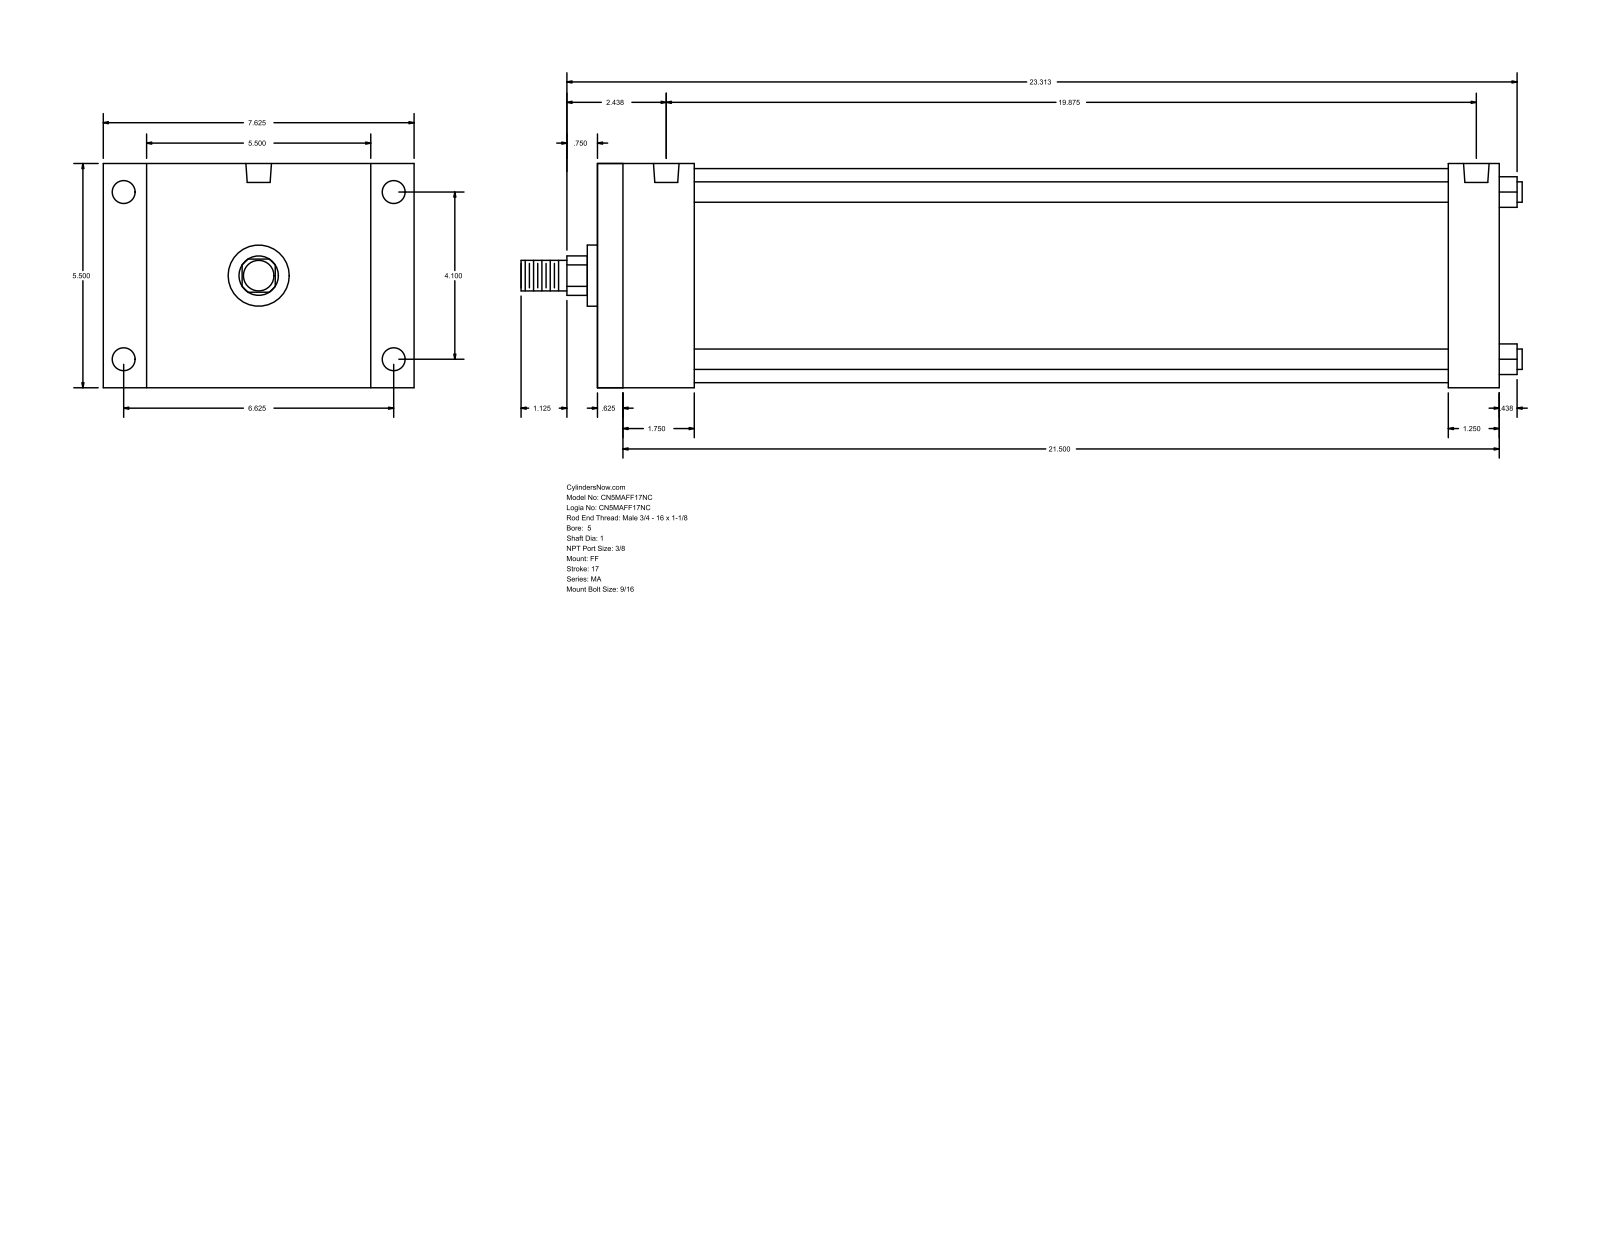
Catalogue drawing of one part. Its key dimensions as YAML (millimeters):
part_name: "MA_FF__0500_1"
step_written_by: "GSSL Pune (CONFIG_CONTROL_DESIGN)"
units: millimeters
bodies: {solids: 0, faces: 92, planar: 64, cylindrical: 28, other: 0}
overall_size: [623.89, 193.68, 139.7]
round_holes:
  - {diameter: 11.11, count: 4}
  - {diameter: 14.29, count: 4}
  - {diameter: 15.93, count: 2}
round_bosses_or_shafts:
  - {diameter: 12.7, count: 4}
  - {diameter: 133.35, count: 1}
  - {diameter: 38.1, count: 1}
  - {diameter: 25.4, count: 1}
  - {diameter: 19.05, count: 1}
partial_cylinders:
  - {radius: 12.29, count: 1}
face_to_face_distances: [139.7, 561.97, 15.87, 546.1, 530.22, 514.35, 31.75, 60.33, 44.46, 469.89]
hole_center_spacings: [4.76, 104.14, 168.28, 197.9, 495.31, 500.07, 504.83]
